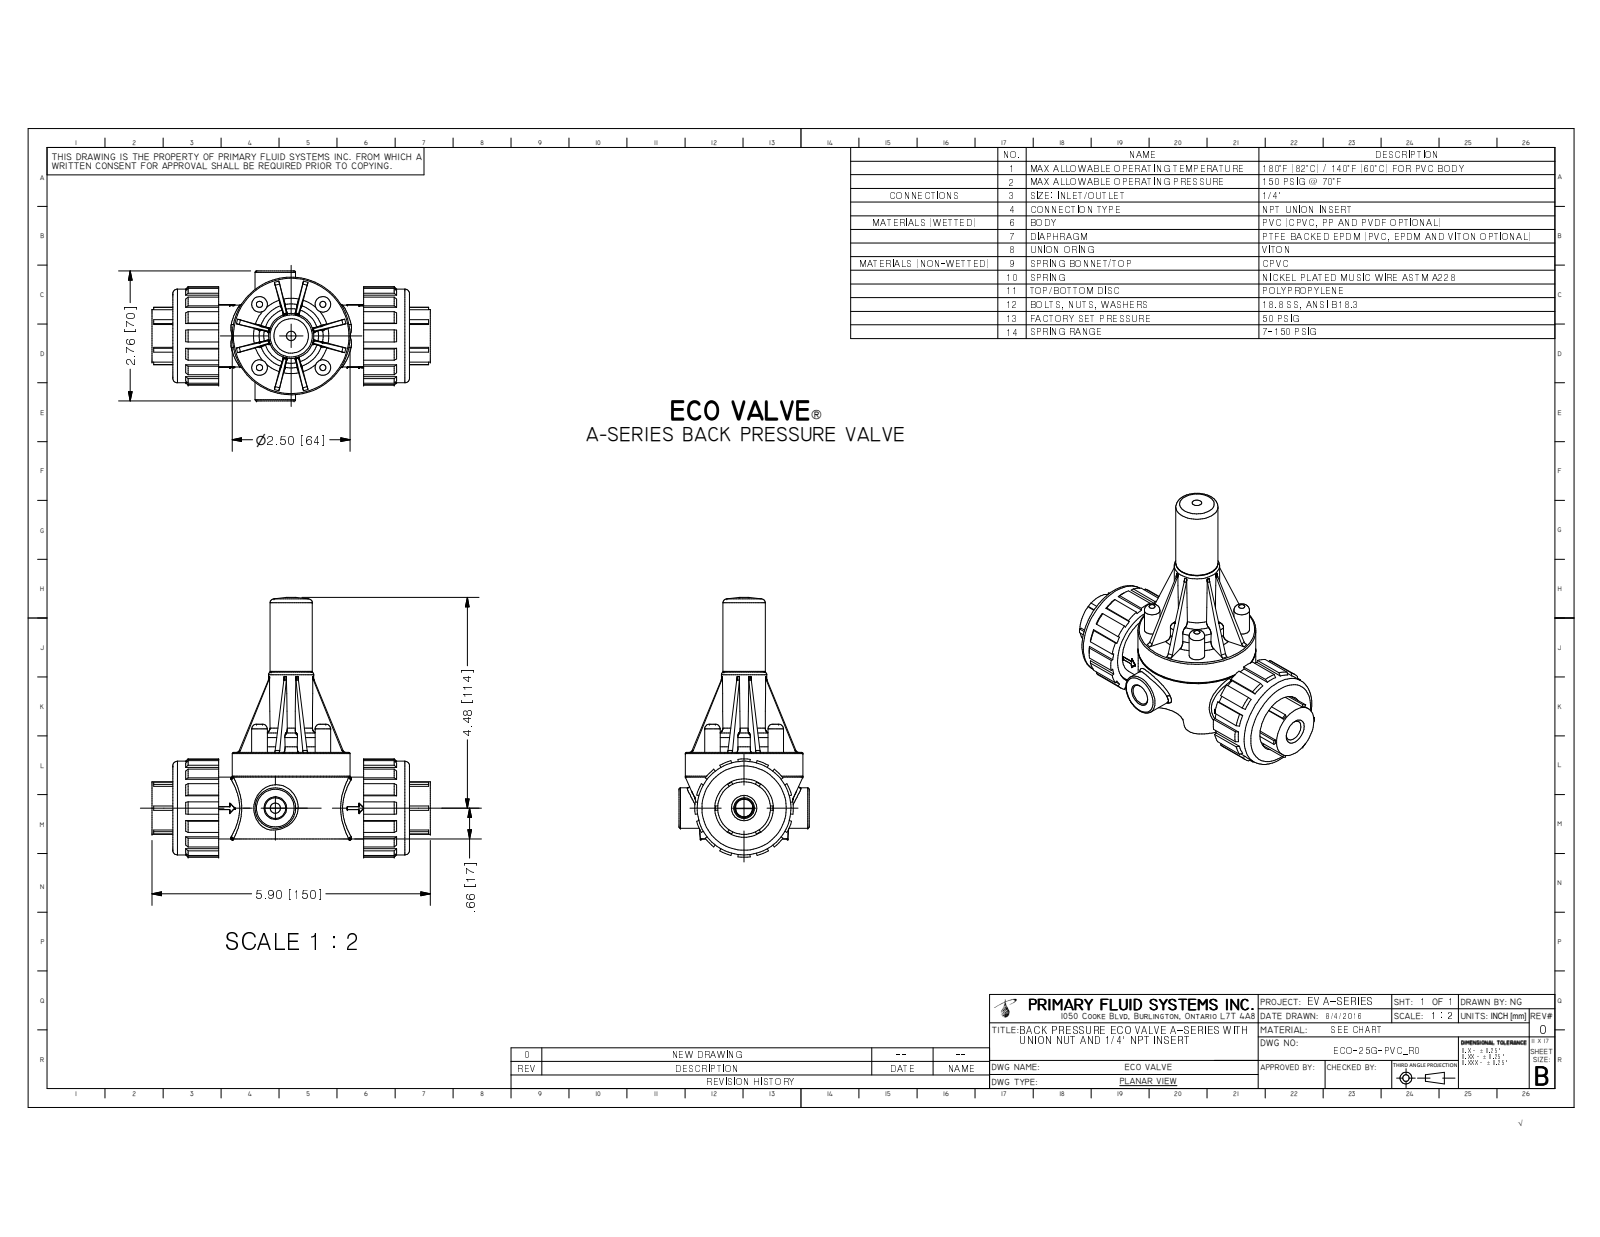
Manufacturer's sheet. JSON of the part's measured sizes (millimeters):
{"part_name": "ECO-25G-PVC_R0", "step_written_by": "Autodesk Inventor 2009 (AUTOMOTIVE_DESIGN)", "units": "millimeters", "bodies": {"solids": 1, "faces": 841, "planar": 264, "cylindrical": 178, "other": 399}, "overall_size": [149.9, 140.2, 70.2], "volume_mm3": 307100, "surface_area_mm2": 69940, "round_holes": [[5.8, 4], [6.5, 4], [10.2, 4], [11.1, 2], [26, 1], [35, 1]], "round_bosses_or_shafts": [[8.4, 4], [6.5, 4], [63.5, 1], [42.9, 1], [38.2, 1], [34.5, 1], [33.4, 1], [29.9, 1]], "partial_cylinders_radius": [[1.8, 8], [2.5, 8], [3.3, 4], [6.5, 4], [7.4, 4], [12.9, 1], [15.5, 1], [16.9, 1]], "face_to_face_distances": [46.7, 21.6, 128.3, 106.7, 149.9, 23.9, 126, 2.3, 104.4, 33.4], "hole_center_spacings": [34.1, 34.1, 34.1, 48.3, 48.3, 34.1, 48.3, 48.3]}
